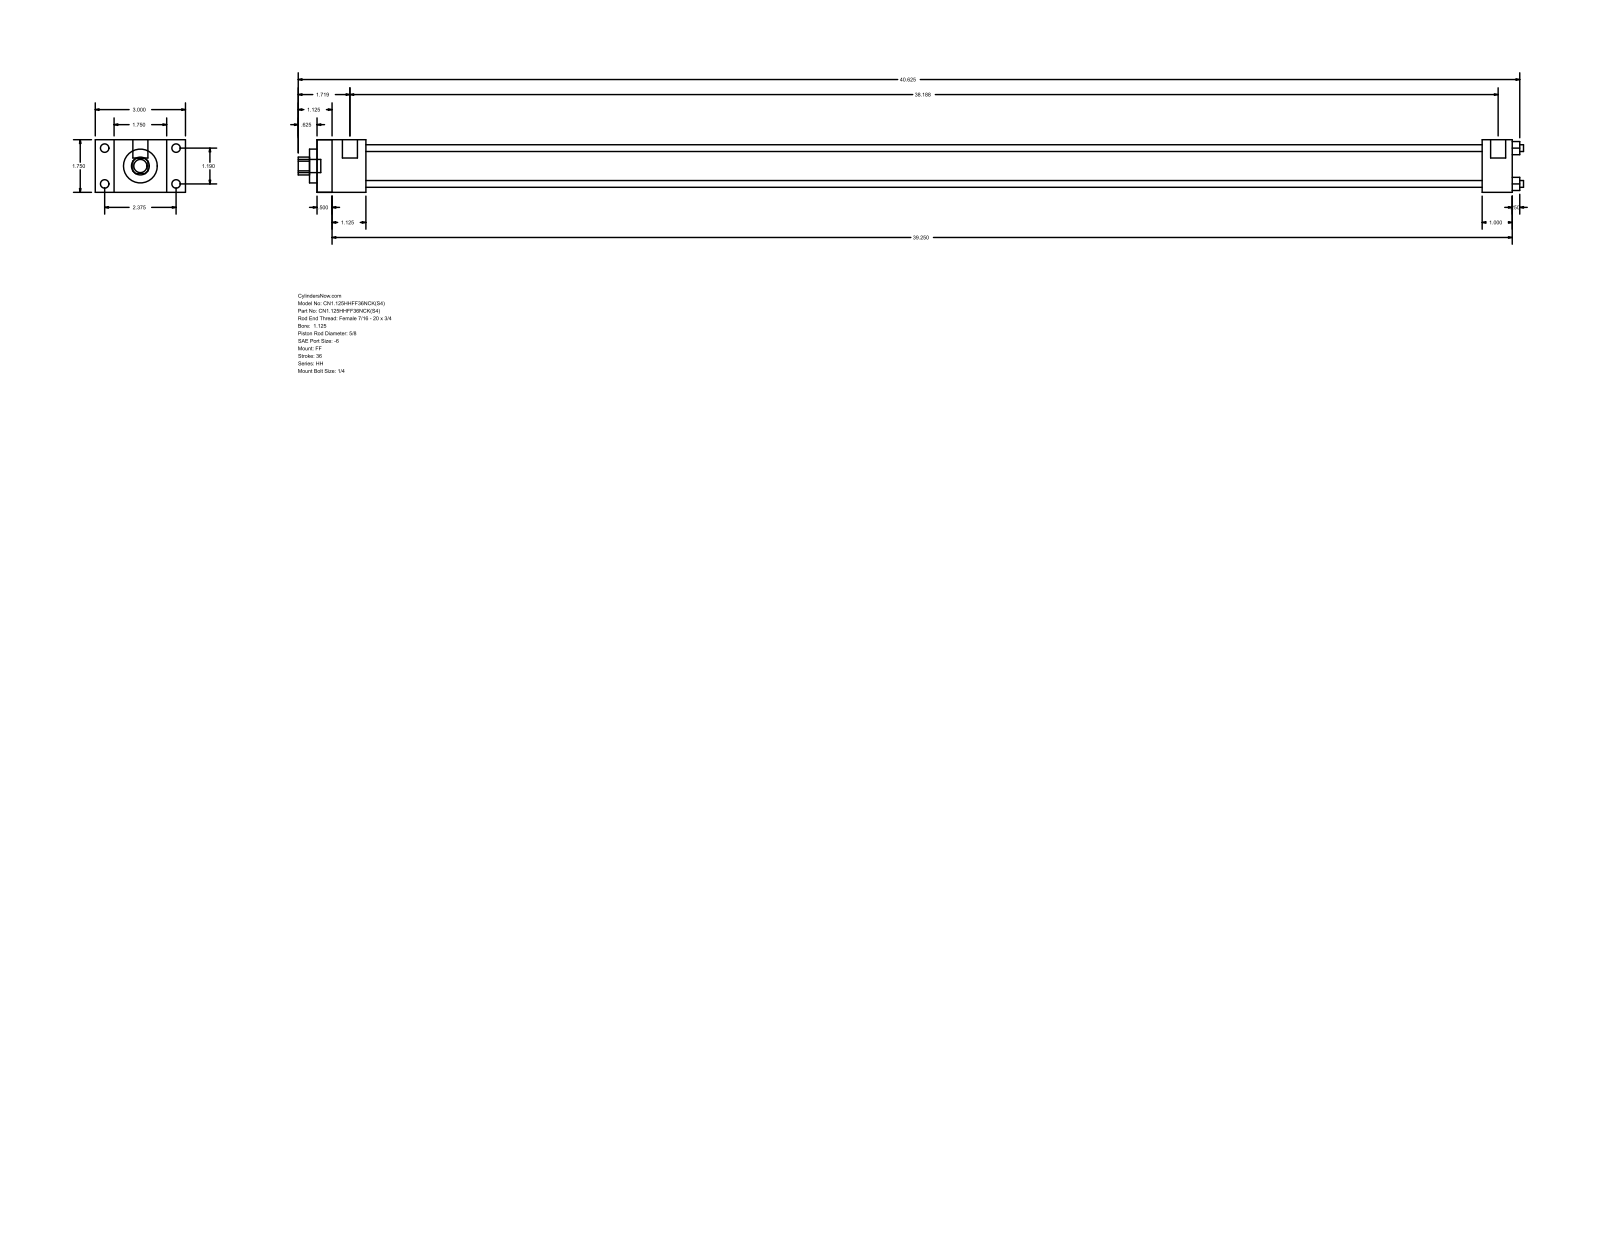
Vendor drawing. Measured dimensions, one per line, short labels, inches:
name: HH_FF__0112_0.625
written by: GSSL Pune (CONFIG_CONTROL_DESIGN)
unit: in
bodies: 0 solids, 92 faces (64 planar, 28 cylindrical, 0 other)
size: 40.75 × 3 × 1.75
holes: 4× ⌀0.225, 1× ⌀0.625, 1× ⌀1.125, 1× ⌀1.375
bosses: 4× ⌀0.281, 4× ⌀0.219, 2× ⌀0.5, 1× ⌀0.437
rounds: 1× R0.297
face distances: 1.75, 39.75, 0.625, 0.5, 39.25, 2.375, 1.125, 1.625, 38.75, 38.25
hole spacings: 0.841, 1.19, 1.683
